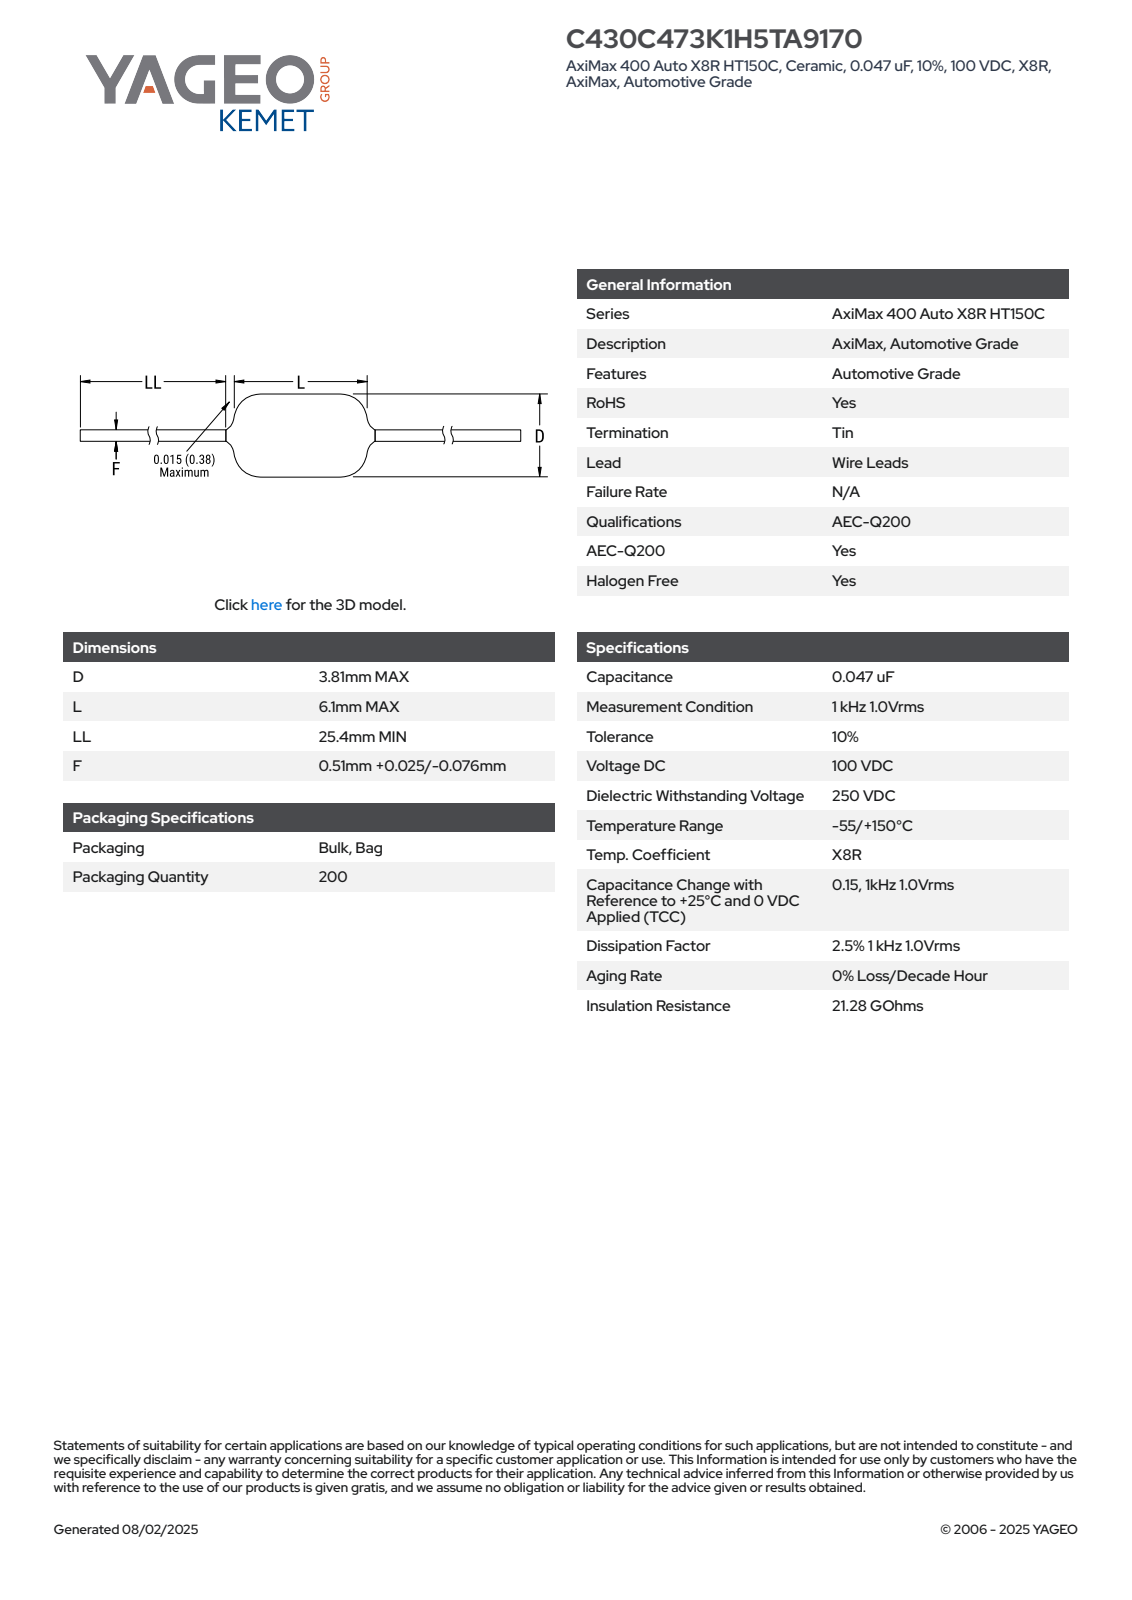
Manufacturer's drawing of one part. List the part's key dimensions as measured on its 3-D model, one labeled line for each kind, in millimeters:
Part name (STEP PRODUCT): CCA_ACST_C430_D3.81L6.1LL25.4F0.535
STEP written by: SolidWorks 2014 (AUTOMOTIVE_DESIGN)
Units: millimetres
Bodies: 1 solid, 74 faces (26 planar, 9 cylindrical, 39 other)
Overall size (bounding box): 57.66 × 3.81 × 3.81
Volume: 79 mm³ · Surface area: 174 mm²
Round bosses / shafts (diameter × count): ⌀3.81 ×1, ⌀0.54 ×1
Partial cylindrical surfaces — rounded edges, fillets, slot ends (radius × count): R1.9 ×1
Main face-to-face distances: 6.1, 25.78, 31.88, 57.66
